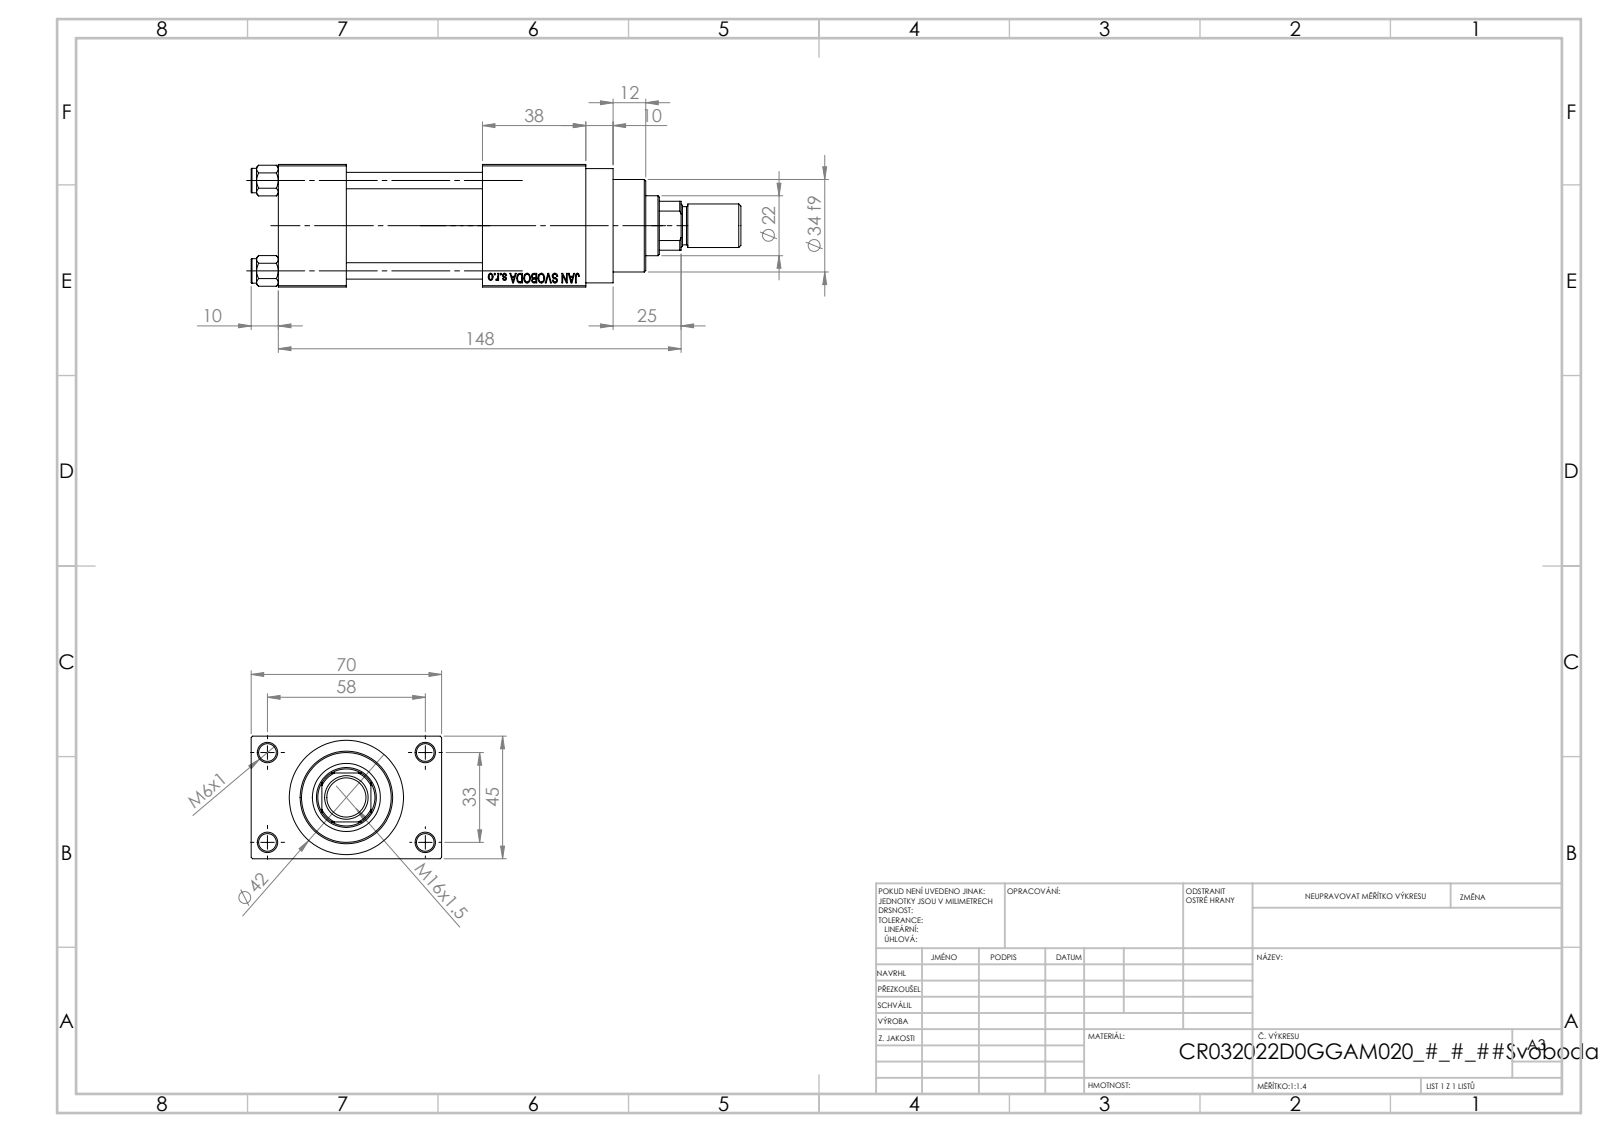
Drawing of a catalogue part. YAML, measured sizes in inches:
part_name: "V215CR_D_Body; V215CR_VCP_D; V215CR_D_TYCINKA; ROD_END_AH (+2 more)"
step_written_by: "SolidWorks 2019 (CONFIG_CONTROL_DESIGN)"
units: inches
bodies: {solids: 12, faces: 1117, planar: 500, cylindrical: 93, other: 524}
overall_size: [7.087, 2.756, 1.772]
volume: 15.19
surface_area: 125.5
round_holes:
  - {diameter: 0.236, count: 4}
  - {diameter: 0.256, count: 4}
  - {diameter: 0.276, count: 2}
  - {diameter: 0.518, count: 2}
  - {diameter: 0.787, count: 2}
  - {diameter: 0.413, count: 1}
  - {diameter: 0.866, count: 1}
  - {diameter: 0.945, count: 1}
  - {diameter: 0.984, count: 1}
  - {diameter: 1.26, count: 1}
  - {diameter: 1.299, count: 1}
round_bosses_or_shafts:
  - {diameter: 0.354, count: 4}
  - {diameter: 1.654, count: 1}
  - {diameter: 1.496, count: 1}
  - {diameter: 1.339, count: 1}
  - {diameter: 0.63, count: 1}
  - {diameter: 0.551, count: 1}
partial_cylinders:
  - {radius: 0.413, count: 1}
face_to_face_distances: [1.772, 0.984, 0.492, 2.264, 1.969, 2.953, 3.465, 2.756, 1.496, 4.449]
hole_center_spacings: [0.488, 0.924, 1.307, 1.314, 1.392, 1.795, 2.219, 1.299]
